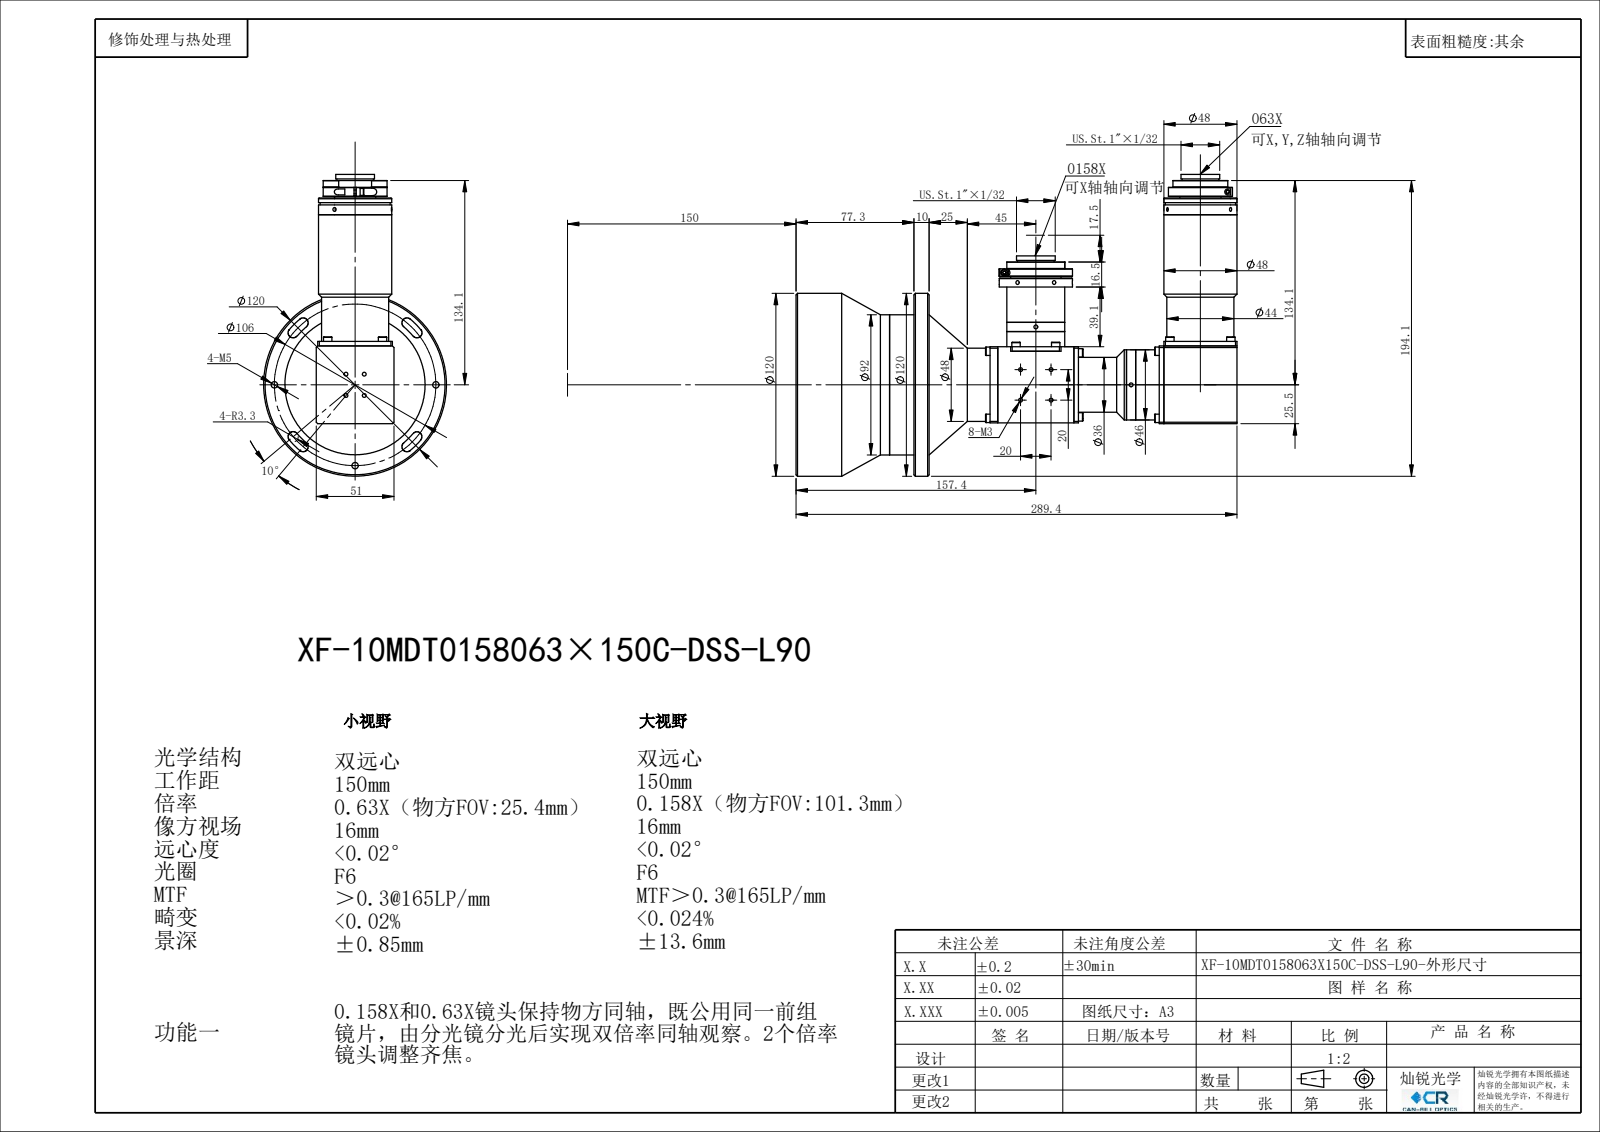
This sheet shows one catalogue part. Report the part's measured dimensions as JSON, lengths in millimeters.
{"part_name": "XF-10MDT0158063X150C-DSS-L90", "step_written_by": "SolidWorks 2018 (CONFIG_CONTROL_DESIGN)", "units": "millimeters", "bodies": {"solids": 0, "faces": 587, "planar": 252, "cylindrical": 207, "other": 128}, "overall_size": [289.36, 198.06, 120], "round_holes": [[2.5, 22], [4.2, 4], [22, 2], [23, 1], [24.4, 1], [25.4, 1], [30, 1], [111, 1], [115, 1]], "round_bosses_or_shafts": [[5.5, 16], [48, 3], [46, 2], [24, 2], [4.5, 2], [120, 1], [92, 1], [44, 1]], "partial_cylinders_radius": [[3.3, 8], [2, 2], [2.5, 1], [3, 1], [18, 1], [21, 1], [49.7, 1], [56.3, 1]], "face_to_face_distances": [0.5, 50.5, 50, 51, 10, 3, 212.02, 202.02, 53, 105.02], "hole_center_spacings": [20, 9.22, 21.21, 30, 46.39, 47.52, 53, 59.41]}
